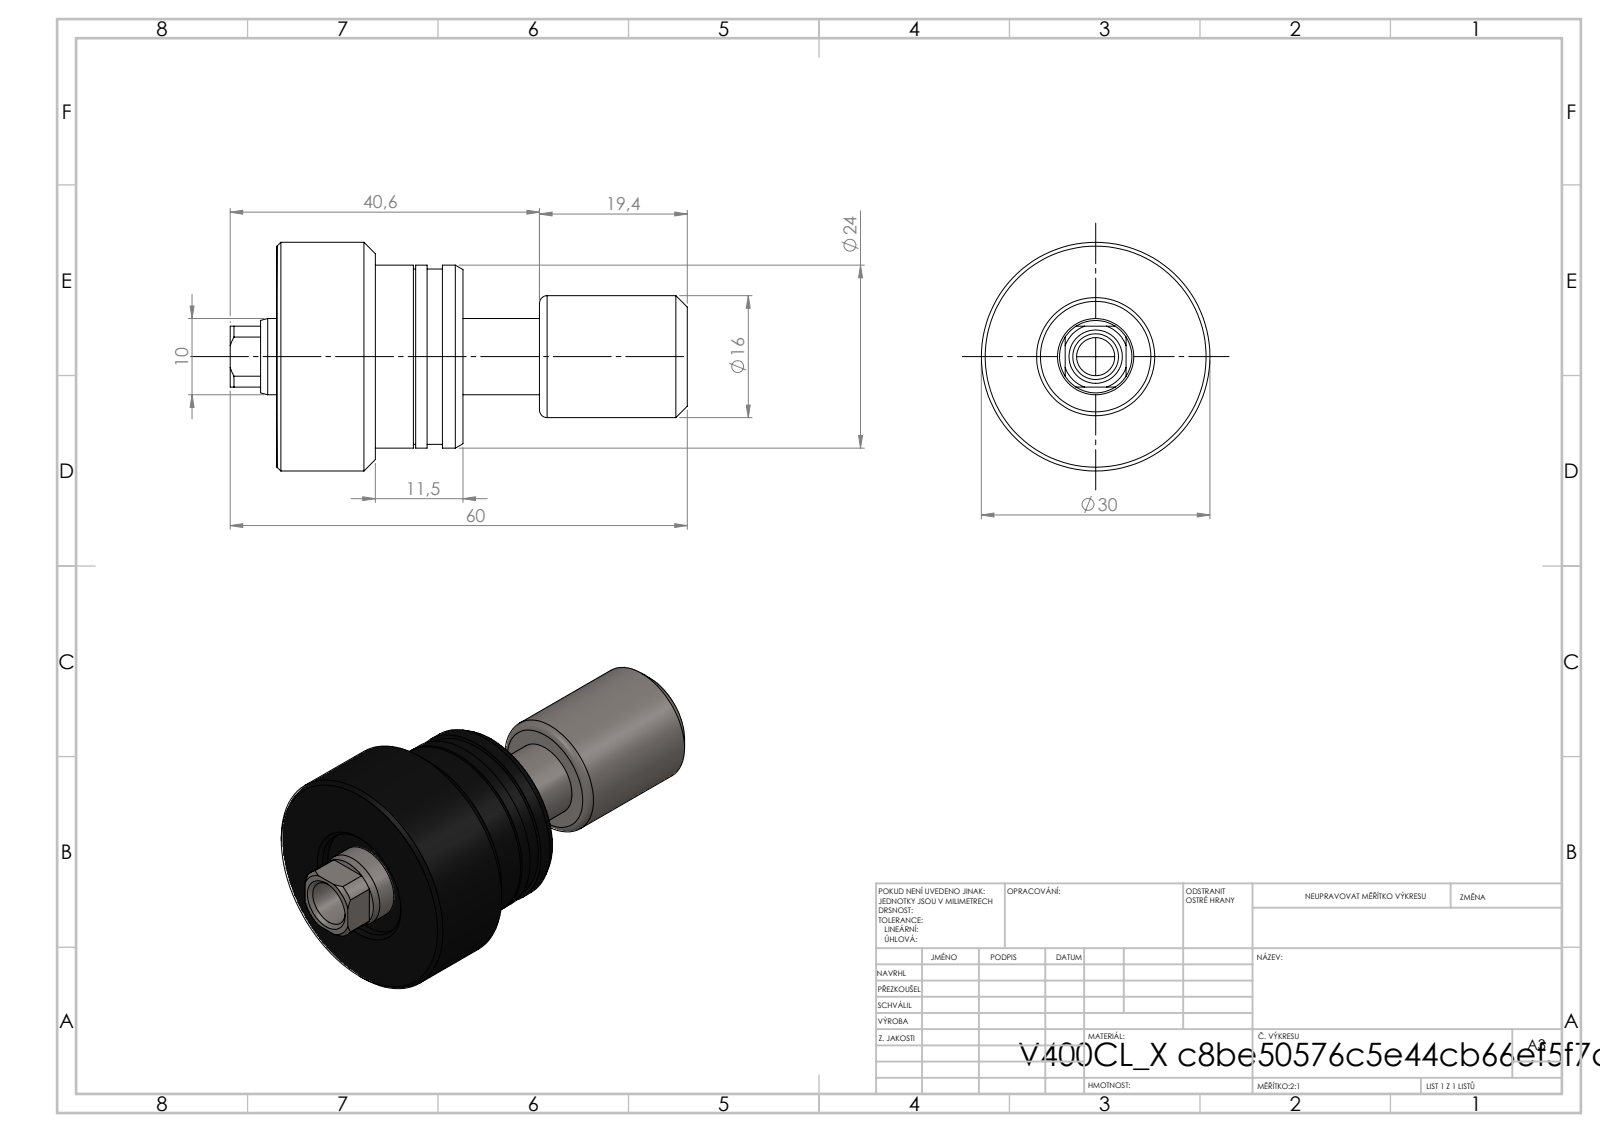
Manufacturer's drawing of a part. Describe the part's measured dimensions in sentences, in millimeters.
The part is named "V400CL_PC_X; V400CL_VC_X". Its 3-D file was written by "SolidWorks 2019 (CONFIG_CONTROL_DESIGN)". It is 2 solids with 79 faces: 19 planar, 30 cylindrical and 30 other. Overall it measures 60 by 30 by 30 millimeters. Its volume is 18 424 cubic millimeters and its surface area 7 057 square millimeters. Round holes: 1 of diameter 2.05, 1 of diameter 5, 1 of diameter 6, 1 of diameter 10, 1 of diameter 14.5. Round bosses or shafts: 1 of diameter 30, 1 of diameter 24, 1 of diameter 23, 1 of diameter 16. Partial cylindrical surfaces (rounded edges, fillets, slot ends): 1 of radius 4.75. The main face-to-face distances are 11.5, 29.45, 40.95, 52.45, 23, 19.4, 10.05, 21.55, 33.05, 8.
